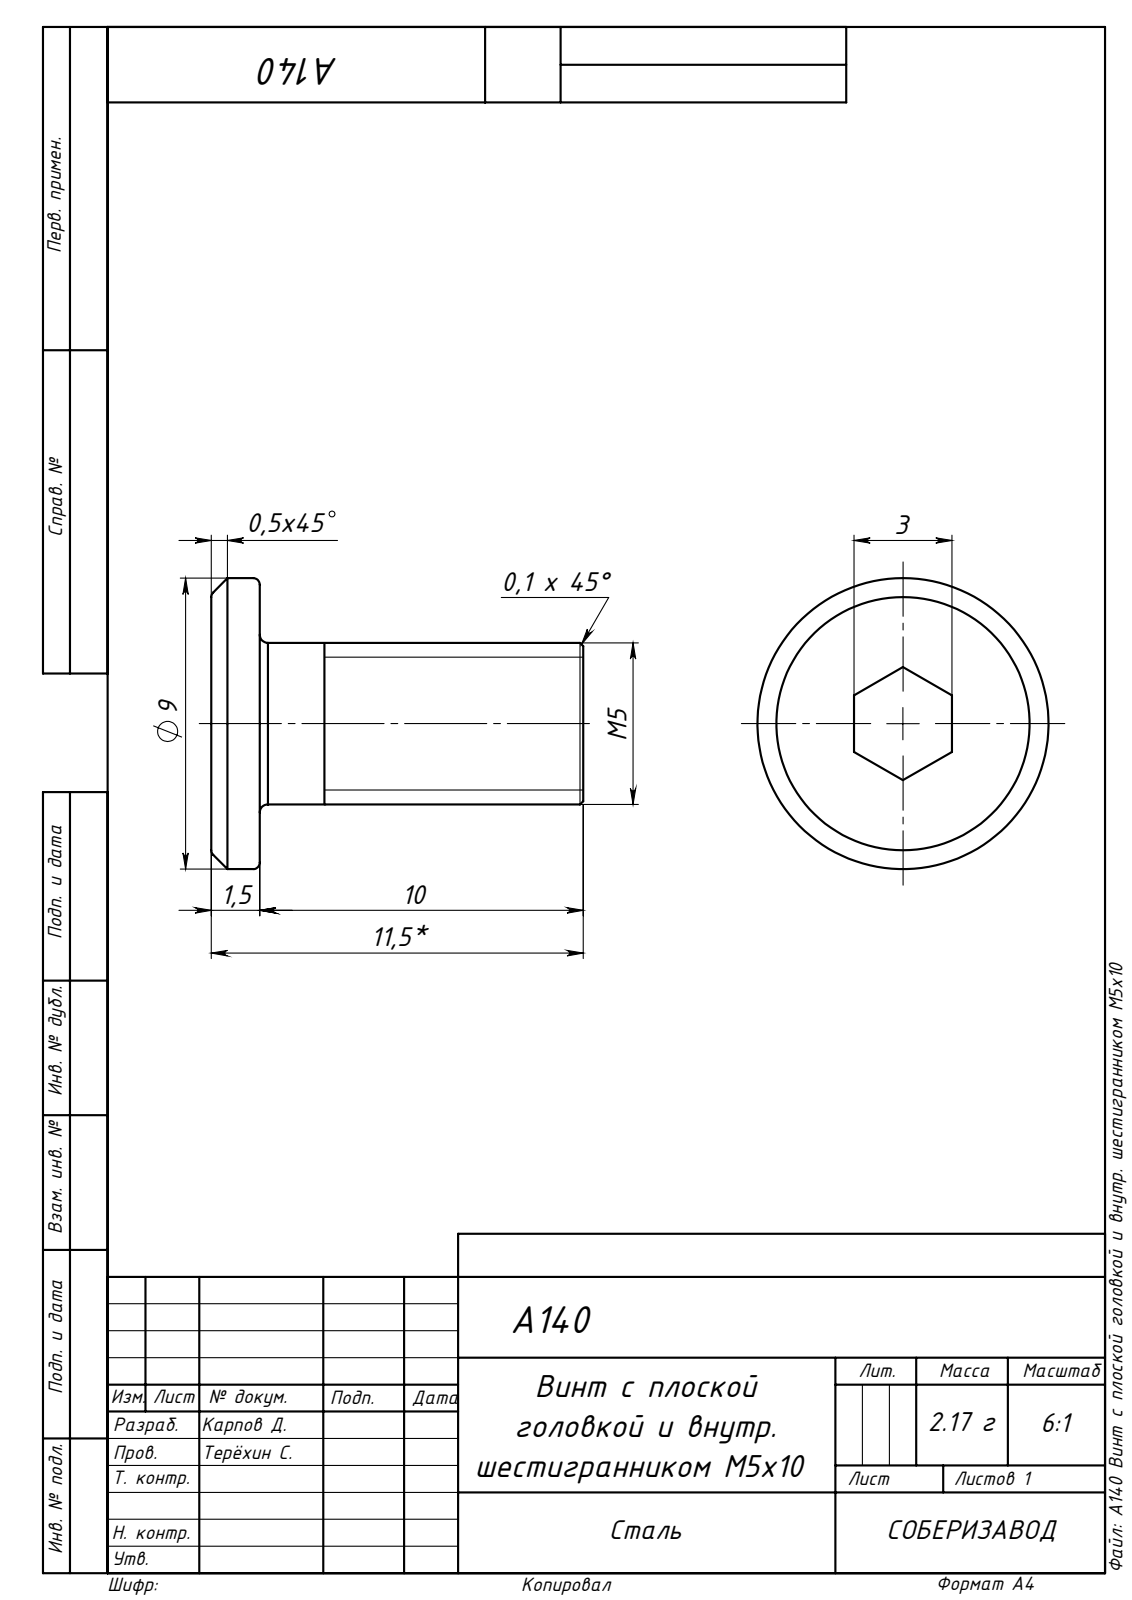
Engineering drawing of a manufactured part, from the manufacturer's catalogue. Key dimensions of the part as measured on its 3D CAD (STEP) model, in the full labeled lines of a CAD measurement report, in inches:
STEP written by: SolidWorks 2020 (AUTOMOTIVE_DESIGN)
Units: inches
Bodies: 1 solid, 24 faces (10 planar, 4 cylindrical, 10 other)
Overall size (bounding box): 0.453 × 0.354 × 0.354
Volume: 0.017 in³ · Surface area: 0.51 in²
Round bosses / shafts (diameter × count): ⌀0.354 ×1, ⌀0.197 ×1
Main face-to-face distances: 0.059, 0.394, 0.453, 0.12
